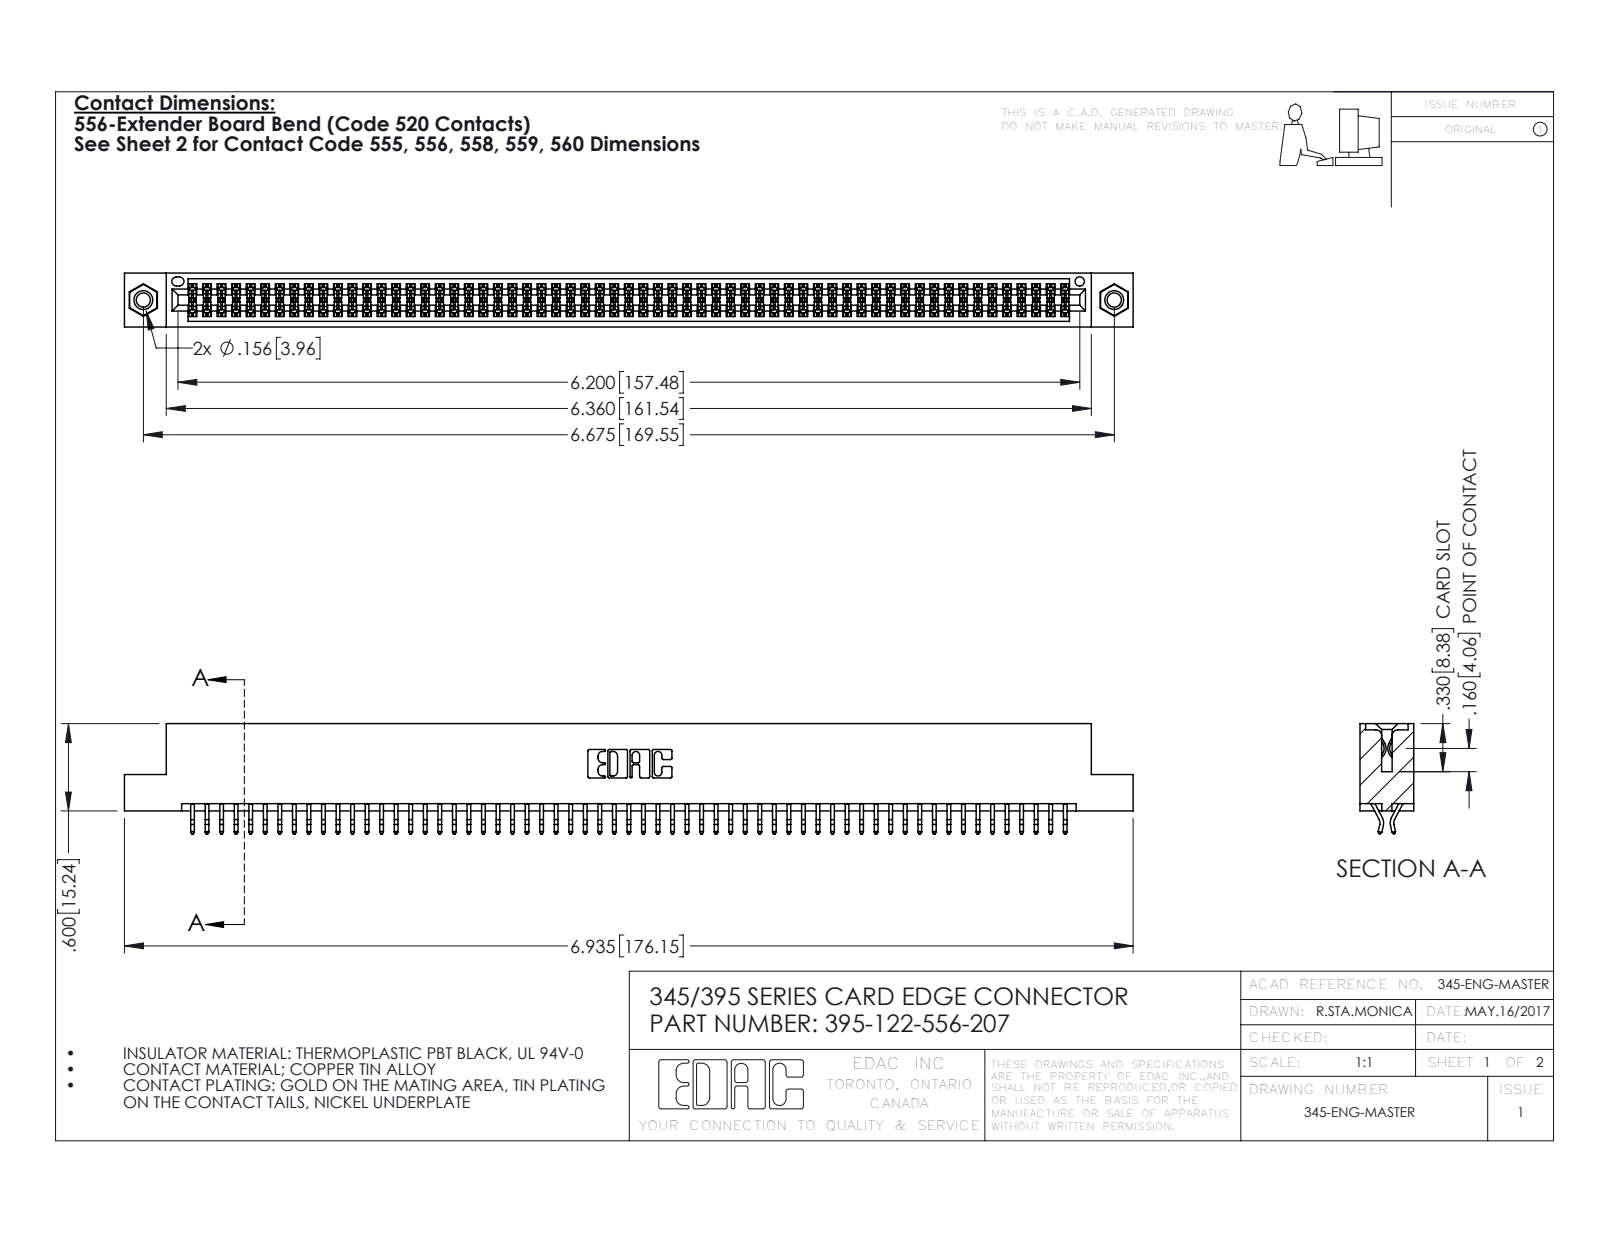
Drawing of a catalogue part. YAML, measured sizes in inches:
part_name: "395-122-556-207; 345 Part_Flush Mounting Lugs - 0.156 Dia-TI; 345-250-001_345-250-005-103; 345-292-001_556 Tail"
step_written_by: "SolidWorks 2016 (CONFIG_CONTROL_DESIGN)"
units: inches
bodies: {solids: 125, faces: 7018, planar: 4626, cylindrical: 2376, other: 16}
overall_size: [6.935, 0.757, 0.37]
volume: 1.054
surface_area: 40.01
round_holes:
  - {diameter: 0.098, count: 2}
  - {diameter: 0.125, count: 2}
  - {diameter: 0.156, count: 2}
  - {diameter: 0.064, count: 1}
round_bosses_or_shafts:
  - {diameter: 0.155, count: 2}
partial_cylinders:
  - {radius: 0.006, count: 183}
  - {radius: 0.01, count: 22}
  - {radius: 0.007, count: 6}
  - {radius: 0.031, count: 6}
  - {radius: 0.026, count: 3}
  - {radius: 0.01, count: 2}
  - {radius: 0.014, count: 2}
  - {radius: 0.019, count: 2}
face_to_face_distances: [0.072, 0.298, 0.37, 0.2, 0.025, 0.098, 0.272, 0.225, 0.175, 0.149]
hole_center_spacings: [0.27, 6.439, 6.675]
